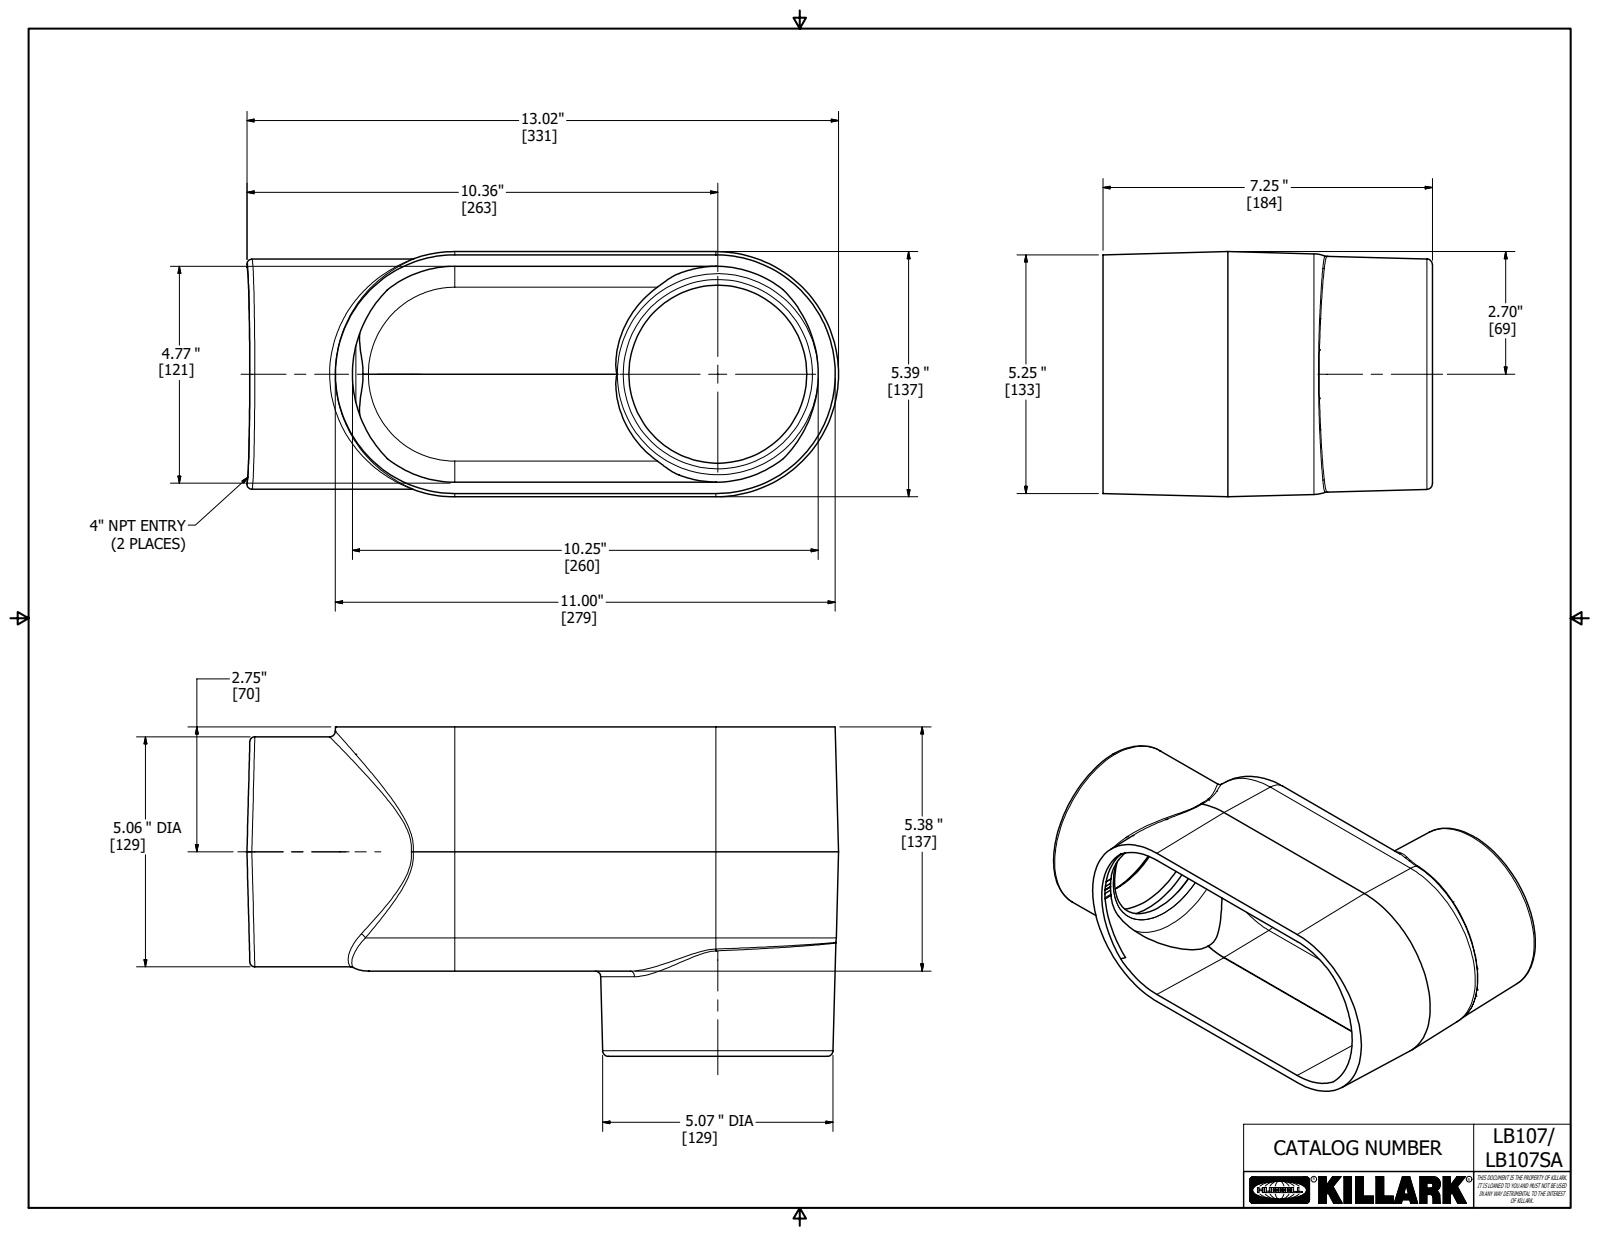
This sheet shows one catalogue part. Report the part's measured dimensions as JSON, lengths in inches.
{"part_name": "17739", "step_written_by": "Autodesk Inventor 2018 (AUTOMOTIVE_DESIGN)", "units": "inches", "bodies": {"solids": 1, "faces": 108, "planar": 36, "cylindrical": 25, "other": 47}, "overall_size": [13.019, 7.25, 5.394], "volume_in3": 63.17, "surface_area_in2": 462.1, "round_holes": [[4.511, 2], [4.719, 1]], "round_bosses_or_shafts": [[5.062, 1]], "partial_cylinders_radius": [[0.05, 6], [0.125, 4], [0.5, 4], [0.75, 2], [2.625, 2], [2.375, 1]], "face_to_face_distances": [0.25, 5.144, 5.394, 4.894, 5.375, 5.125, 0.031, 0.219, 5.344, 1.875]}
